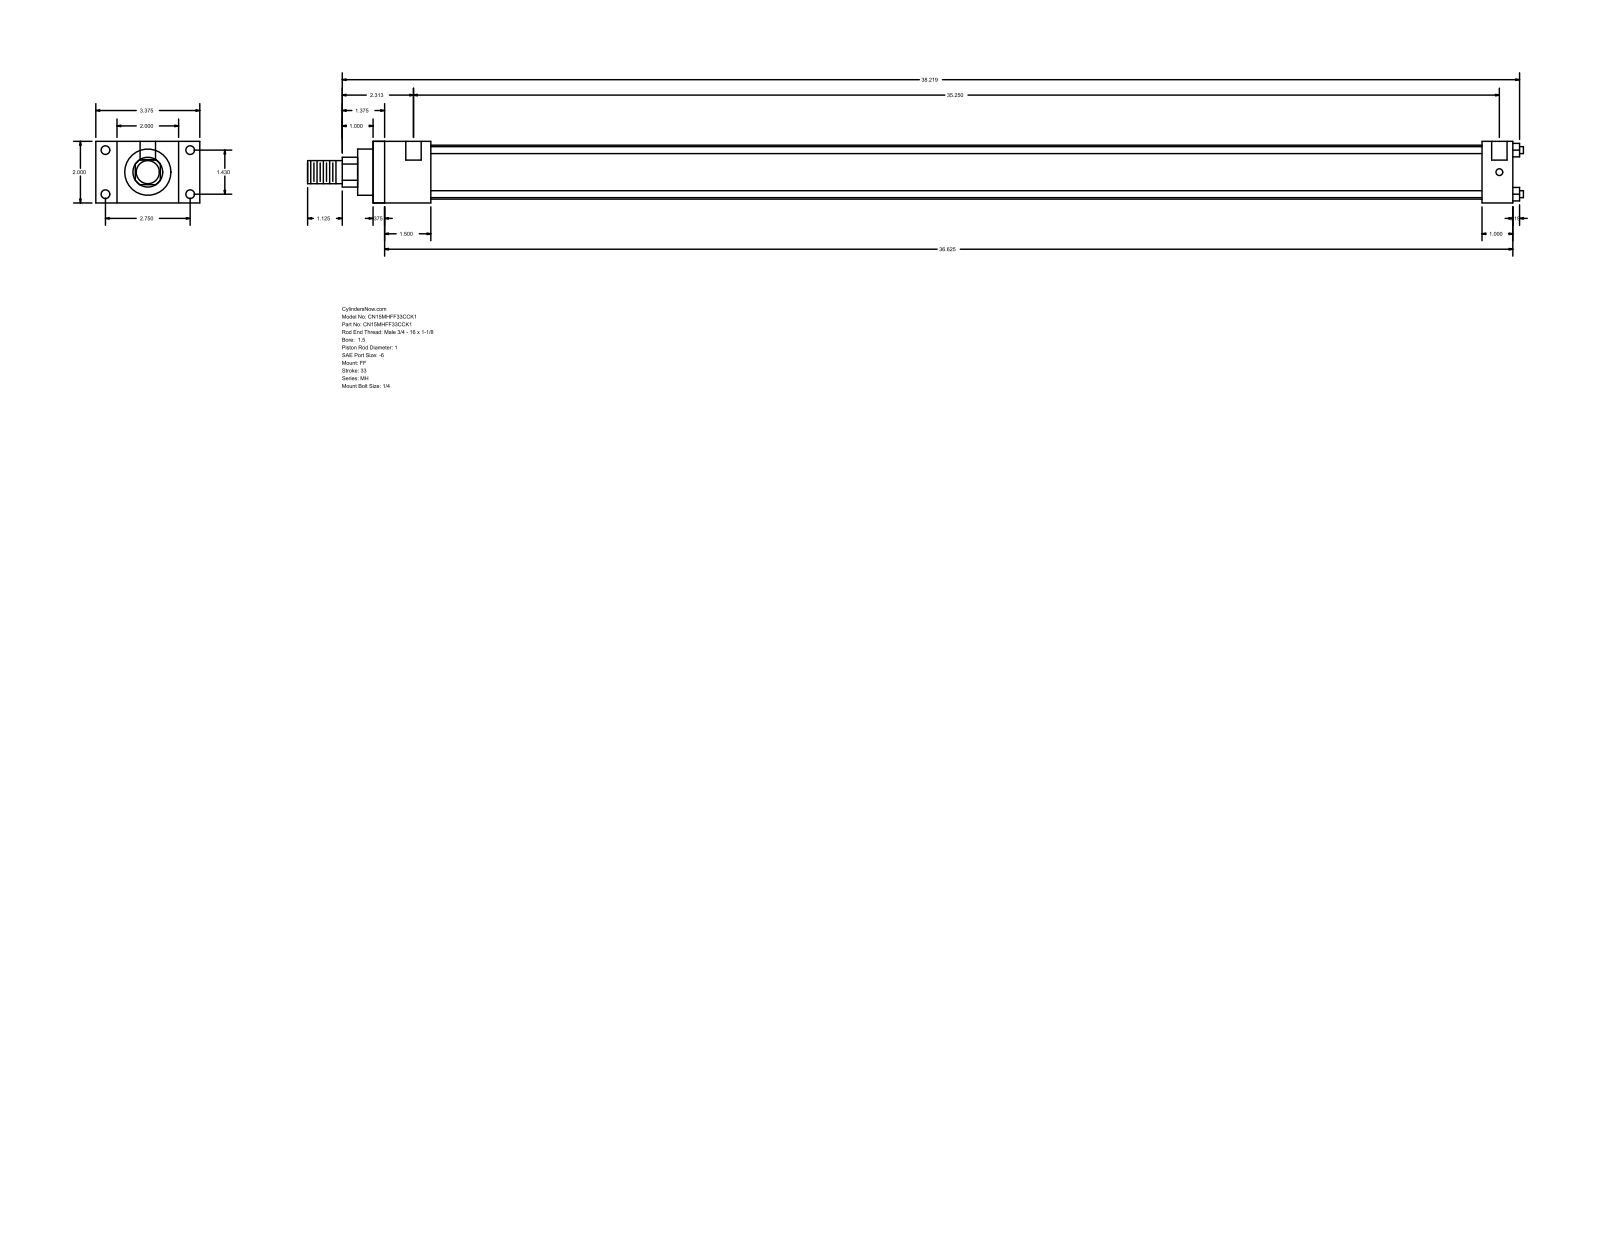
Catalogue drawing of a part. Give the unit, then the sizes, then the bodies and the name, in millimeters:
Units: millimetres
Overall size (bounding box): 1002.51 × 85.72 × 50.8
Round holes (diameter × count): ⌀5.56 ×4, ⌀7.14 ×4, ⌀12.7 ×2
Round bosses / shafts (diameter × count): ⌀5.71 ×4, ⌀44.45 ×1, ⌀38.1 ×1, ⌀25.4 ×1, ⌀19.05 ×1
Partial cylindrical surfaces — rounded edges, fillets, slot ends (radius × count): R12.29 ×1
Main face-to-face distances: 50.8, 939.8, 9.52, 930.28, 25.4, 17.46, 68.26, 47.63, 38.11, 892.17
Hole centre spacings: 36.32, 69.84, 78.72, 898.53, 3.18, 895.35
Bodies: 0 solids, 92 faces (64 planar, 28 cylindrical, 0 other)
Part name (STEP PRODUCT): MH_FF__0150_1
STEP written by: GSSL Pune (CONFIG_CONTROL_DESIGN)
